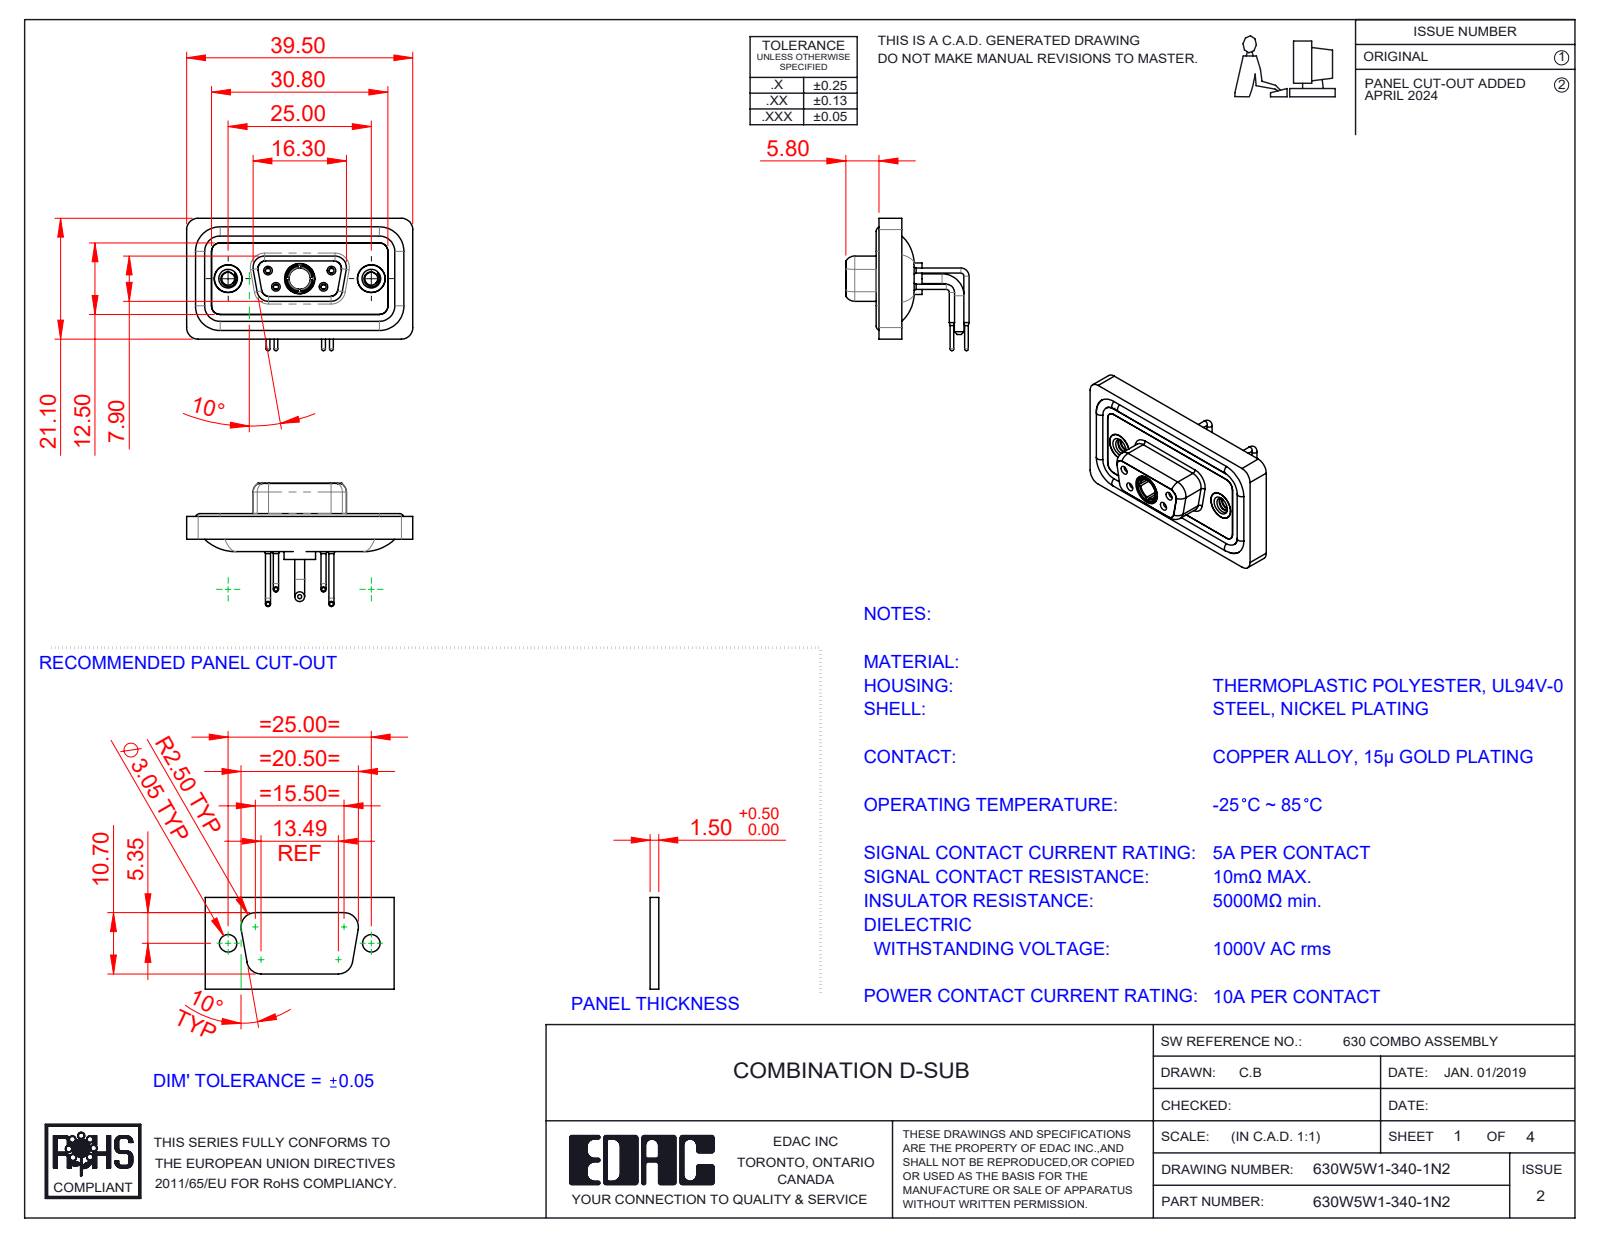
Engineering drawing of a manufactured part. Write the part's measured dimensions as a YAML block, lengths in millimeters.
part_name: "630Combo Waterproof Housing_09 Contacts; 630Combo Contact Row 1_50 Contacts; 630W5W1-340-1N2; Power Socket_10A RA (+5 more)"
step_written_by: "SolidWorks 2023 (CONFIG_CONTROL_DESIGN)"
units: millimeters
bodies: {solids: 13, faces: 676, planar: 194, cylindrical: 305, other: 177}
overall_size: [39.5, 23.12, 21.53]
volume: 4771
surface_area: 7792
round_holes:
  - {diameter: 0.9, count: 4}
  - {diameter: 1.1, count: 4}
  - {diameter: 1.5, count: 4}
  - {diameter: 2, count: 4}
  - {diameter: 4.85, count: 3}
  - {diameter: 1.6, count: 2}
  - {diameter: 1.7, count: 2}
  - {diameter: 2.26, count: 2}
  - {diameter: 4, count: 2}
  - {diameter: 4.05, count: 2}
  - {diameter: 5, count: 2}
  - {diameter: 3.7, count: 1}
round_bosses_or_shafts:
  - {diameter: 1.6, count: 6}
  - {diameter: 0.9, count: 4}
  - {diameter: 0.65, count: 4}
  - {diameter: 4.95, count: 2}
  - {diameter: 4.8, count: 2}
  - {diameter: 1.7, count: 2}
  - {diameter: 5.5, count: 1}
  - {diameter: 5.2, count: 1}
partial_cylinders:
  - {radius: 1.5, count: 18}
  - {radius: 2, count: 18}
  - {radius: 1.35, count: 8}
  - {radius: 1.6, count: 8}
  - {radius: 0.25, count: 4}
  - {radius: 0.5, count: 4}
  - {radius: 0.6, count: 4}
  - {radius: 0.65, count: 4}
face_to_face_distances: [0.4, 1.8, 1.1, 2.9, 2.5, 1.6, 3.1, 1.5, 2.1, 0.5]
hole_center_spacings: [3.16, 5.72, 7.1, 12.5, 18.1, 4.39, 4.4, 8.31]
